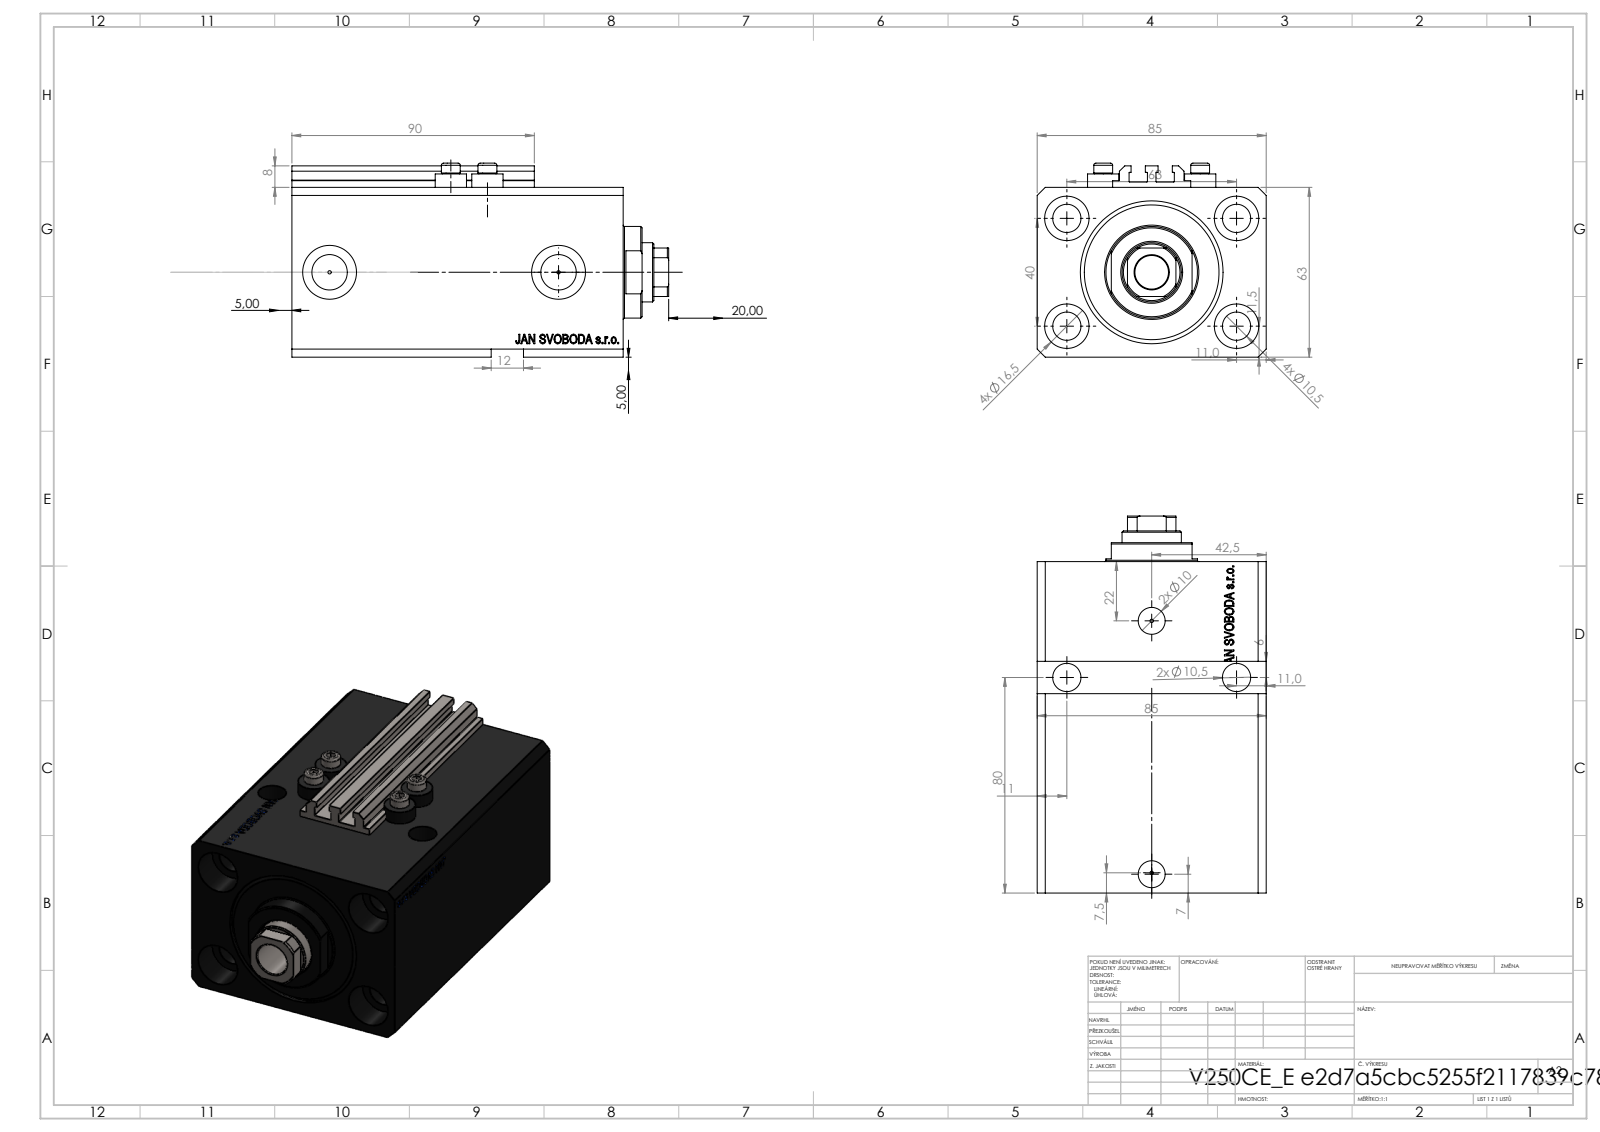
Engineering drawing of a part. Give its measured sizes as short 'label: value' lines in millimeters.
name: V250CE_VC_E; V250CE_E_Body; ALLEN BOLT V250CE; V250CE_C_VCP
written by: SolidWorks 2019 (CONFIG_CONTROL_DESIGN)
unit: mm
bodies: 8 solids, 1107 faces (535 planar, 146 cylindrical, 426 other)
size: 140 × 85 × 72
volume: 556 639 mm³; area: 119 327 mm²
holes: 8× ⌀10.5, 4× ⌀1.25, 4× ⌀4, 4× ⌀16.5, 2× ⌀10, 2× ⌀13.16, 2× ⌀20, 1× ⌀12.5, 1× ⌀22, 1× ⌀40, 1× ⌀53
bosses: 4× ⌀11.6, 4× ⌀7, 1× ⌀34
rounds: 10× R0.2, 1× R10.5
face distances: 63, 85, 123, 17, 106, 11.4, 94.6, 111.6, 3, 56
hole spacings: 37.31, 63, 13.6, 15.4, 24.96, 27.54, 33.62, 36
